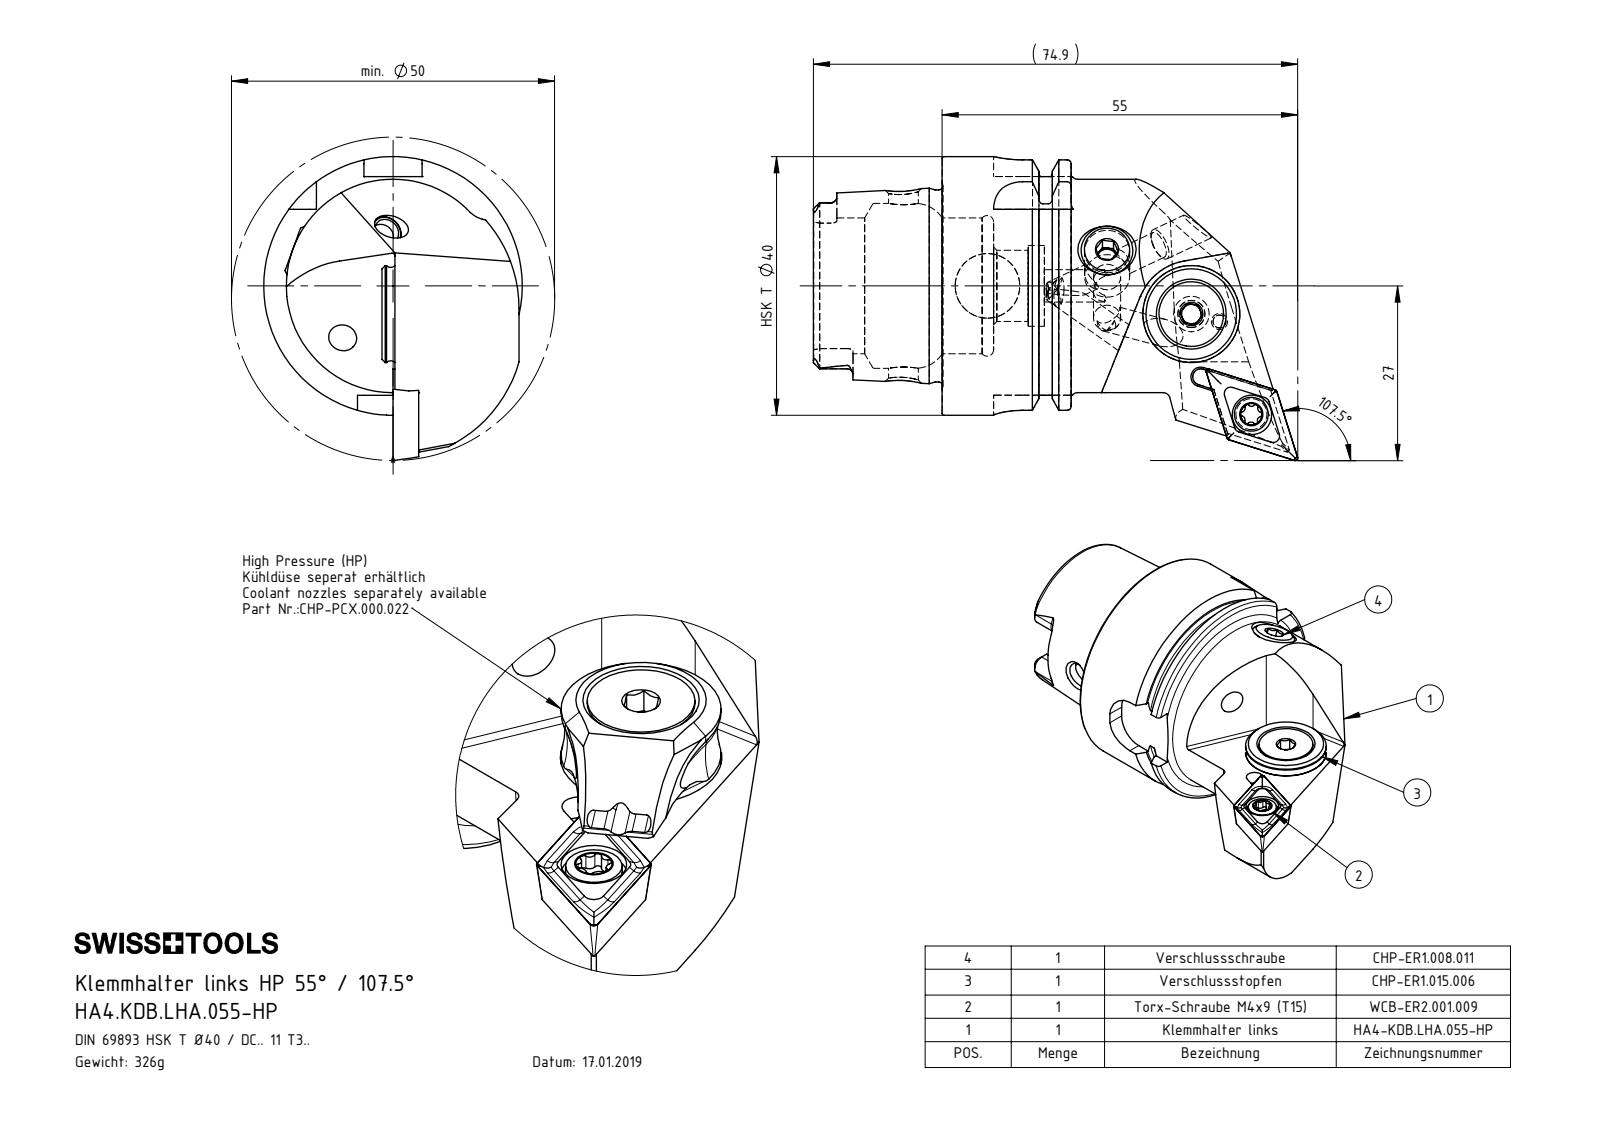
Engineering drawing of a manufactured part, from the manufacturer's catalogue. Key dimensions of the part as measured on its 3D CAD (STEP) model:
Part name (STEP PRODUCT): HA4-KDB.LHA.055-HP_B_Fertigbearbeitung; DIN 3771 - 13x1; DIN 7991 - M5x18_mit gewinde; CHP-PCX.000.022_Dse (+8 more)
STEP written by: SolidWorks 2017 (AUTOMOTIVE_DESIGN)
Units: millimetres
Bodies: 11 solids, 611 faces (132 planar, 201 cylindrical, 278 other)
Overall size (bounding box): 74.91 × 47 × 40
Volume: 41 659 mm³ · Surface area: 17 431 mm²
Round holes (diameter × count): ⌀4.2 ×5, ⌀5 ×2, ⌀1.2 ×1, ⌀2 ×1, ⌀3 ×1, ⌀3.3 ×1, ⌀4 ×1, ⌀4.4 ×1, ⌀4.6 ×1, ⌀5.3 ×1, ⌀6.1 ×1, ⌀7 ×1
Round bosses / shafts (diameter × count): ⌀5 ×2, ⌀40 ×1, ⌀34.75 ×1, ⌀33 ×1, ⌀29.71 ×1, ⌀14.85 ×1, ⌀13.4 ×1, ⌀10 ×1
Partial cylindrical surfaces — rounded edges, fillets, slot ends (radius × count): R1 ×7, R0.34 ×6, R0.59 ×6, R0.9 ×6, R0.5 ×4, R4.5 ×4, R6 ×3, R1.1 ×2
Main face-to-face distances: 7.95, 4.5, 19.95, 12, 0.83, 3.67, 19.9, 27.85, 39.85, 1.5
Hole centre spacings: 4.5, 15.15, 15.26, 18.05, 18.18, 31.84, 36.31, 45.39
